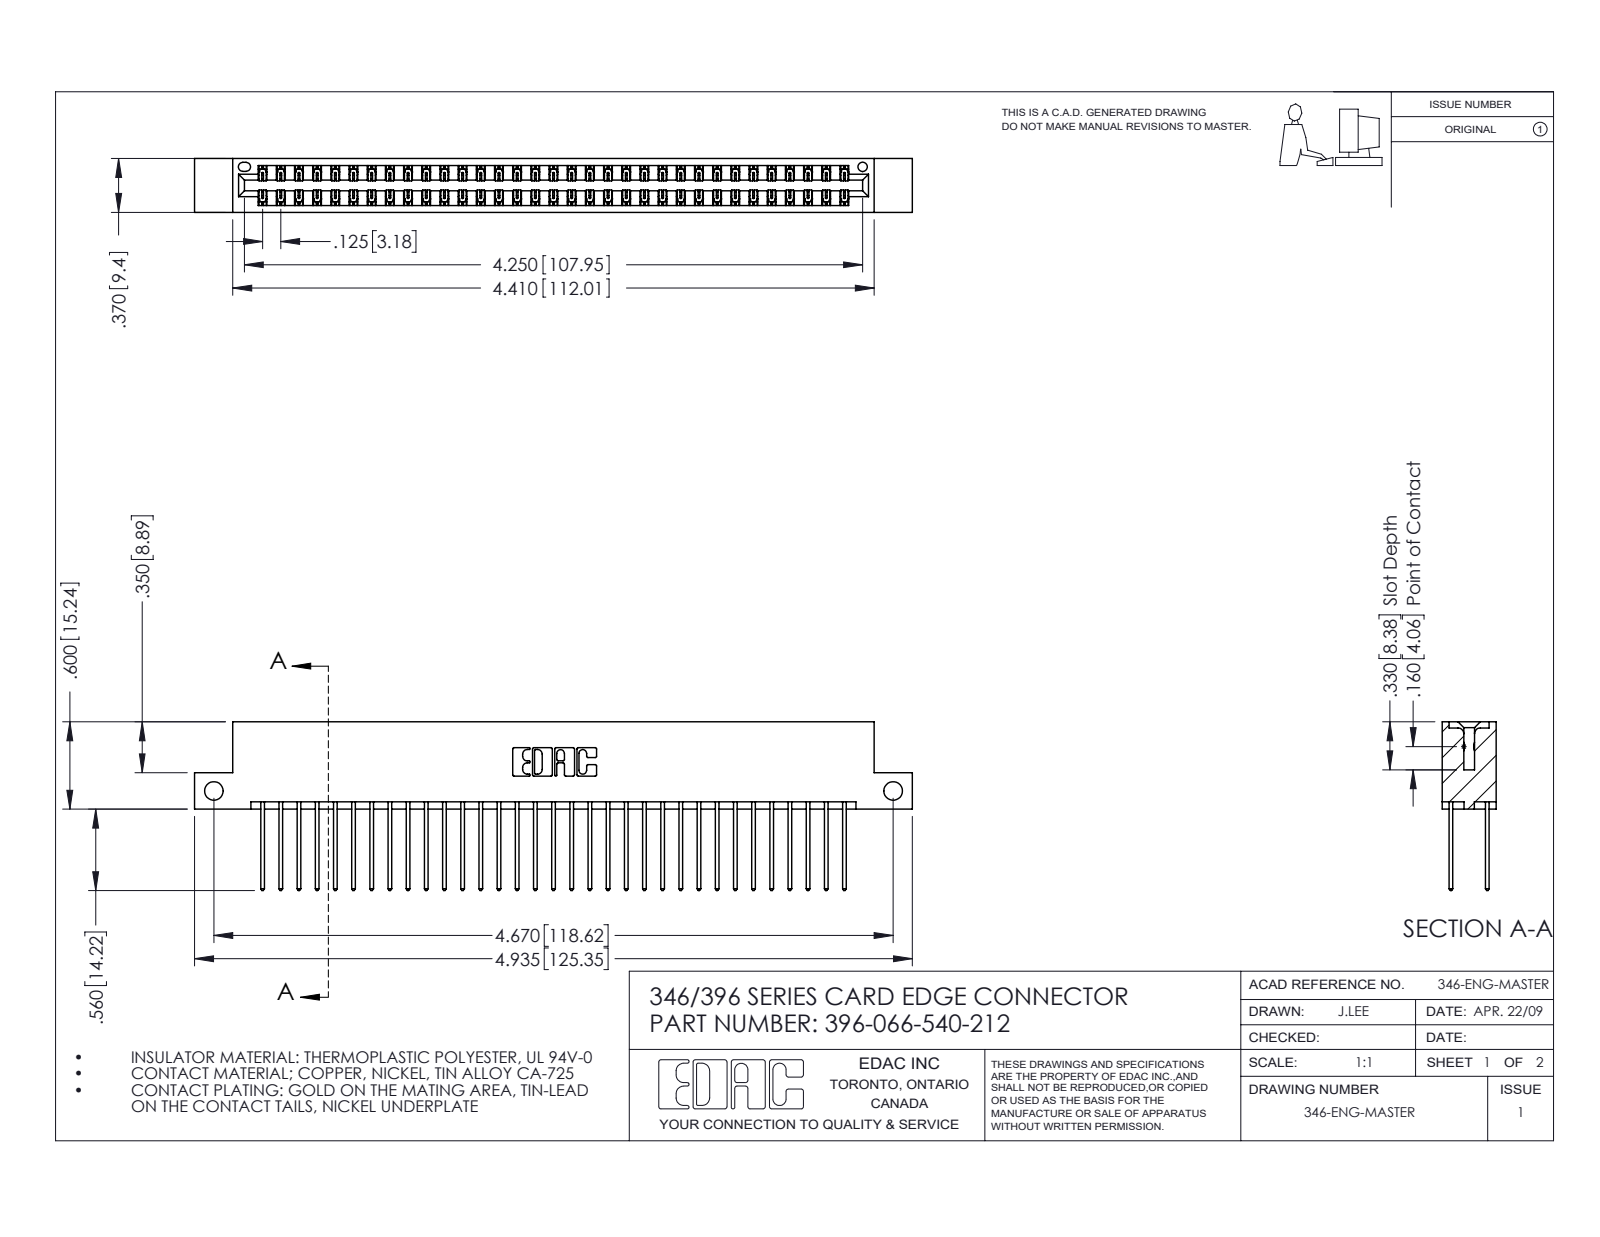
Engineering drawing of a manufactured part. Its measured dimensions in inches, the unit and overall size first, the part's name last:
Units: inches
Overall size (bounding box): 4.935 × 1.16 × 0.37
Round holes (diameter × count): ⌀0.128 ×2, ⌀0.064 ×1
Partial cylindrical surfaces — rounded edges, fillets, slot ends (radius × count): R0.006 ×99, R0.01 ×66, R0.01 ×22, R0.007 ×6, R0.031 ×6, R0.026 ×3, R0.014 ×2, R0.022 ×2
Main face-to-face distances: 0.048, 0.322, 0.25, 0.072, 0.298, 0.025, 0.37, 0.275, 0.148, 0.222
Hole centre spacings: 4.67
Volume: 0.752 in³ · Surface area: 27.64 in²
Bodies: 67 solids, 3554 faces (2386 planar, 1168 cylindrical, 0 other)
Part name (STEP PRODUCT): 345-292-001_345-293-140; 346 Part_Flush Mounting Lugs - Side Mount; 396-066-540-212
STEP written by: SolidWorks 2016 (CONFIG_CONTROL_DESIGN)
